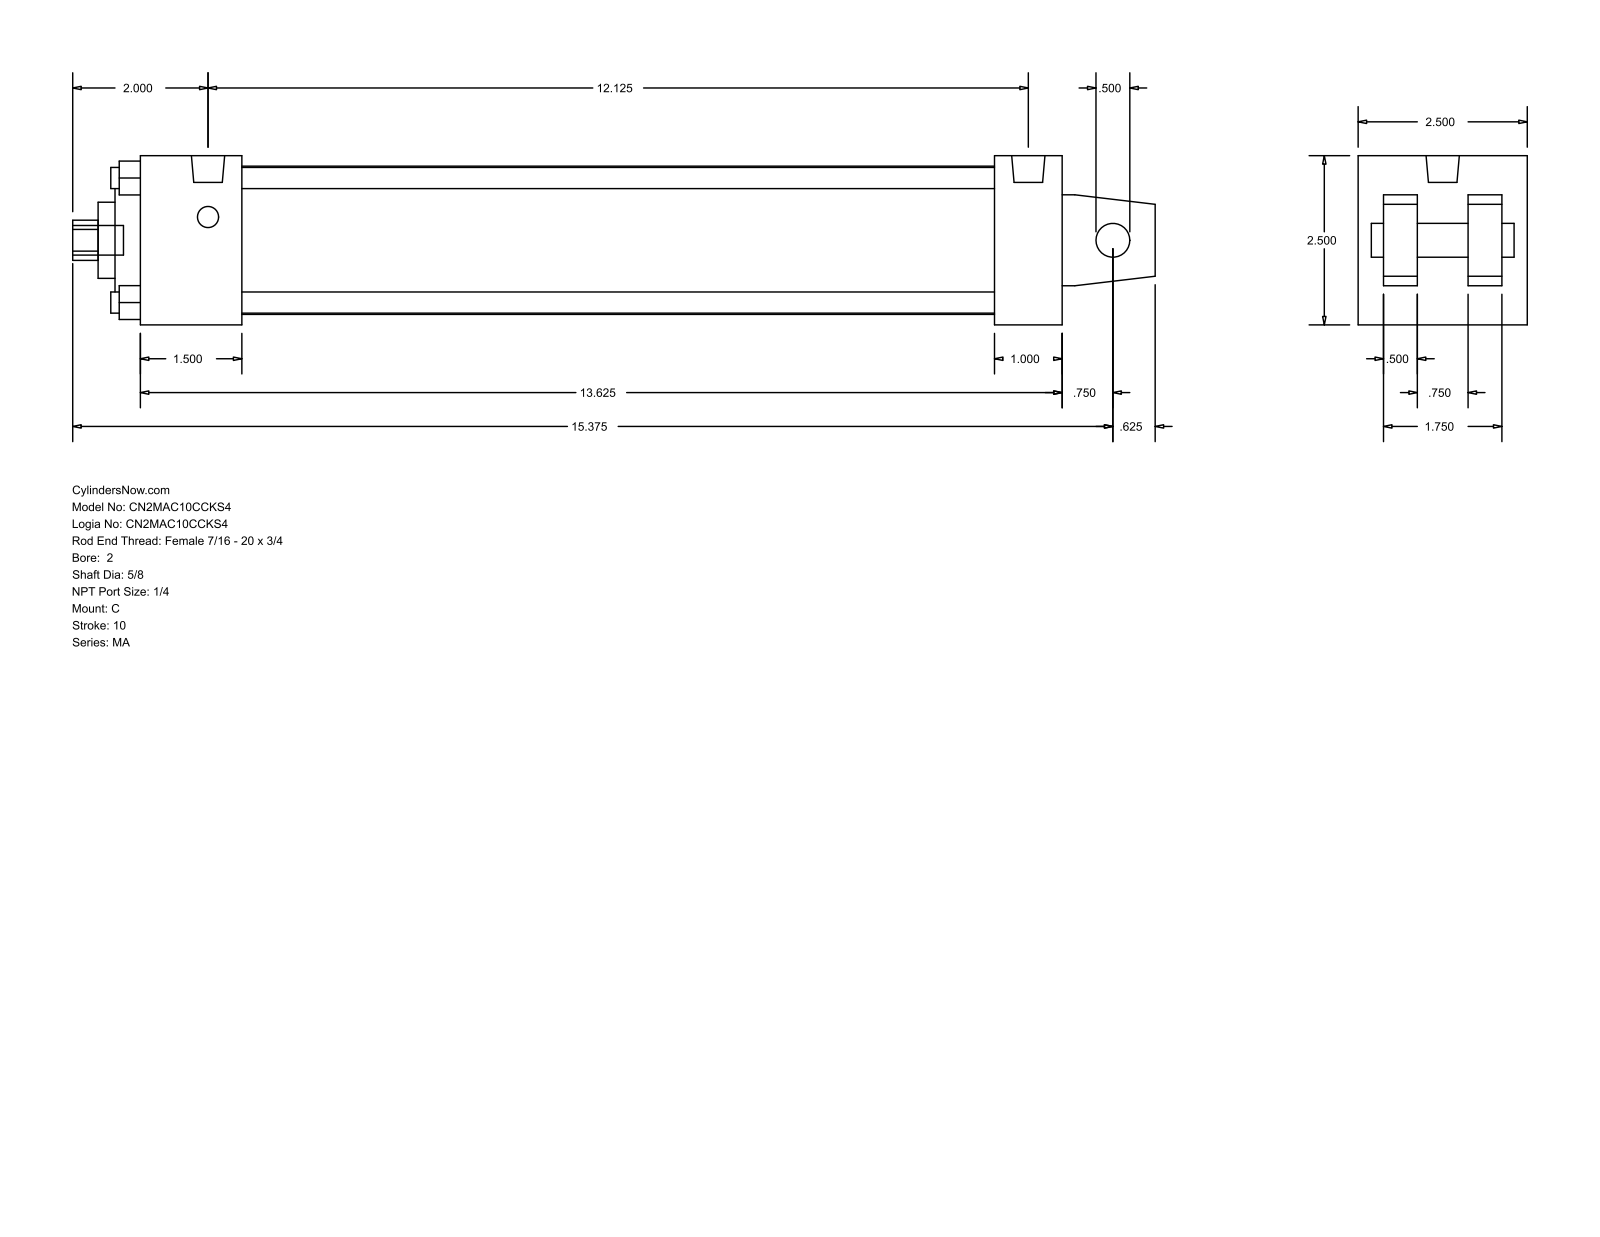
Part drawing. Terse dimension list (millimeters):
name: MA_C__0200_0.625
written by: GSSL Pune (CONFIG_CONTROL_DESIGN)
unit: mm
bodies: 0 solids, 105 faces (77 planar, 28 cylindrical, 0 other)
size: 406.4 × 63.5 × 63.5
holes: 4× ⌀7.94, 1× ⌀12.7, 1× ⌀15.88, 1× ⌀28.57, 1× ⌀50.8, 1× ⌀55.63
bosses: 4× ⌀7.94, 2× ⌀12.49, 1× ⌀11.11
rounds: 1× R7.54
face distances: 63.5, 9.52, 12.7, 22.22, 41.28, 53.98, 31.76, 38.1, 346.08, 307.98
hole spacings: 33.05, 46.74, 66.1
